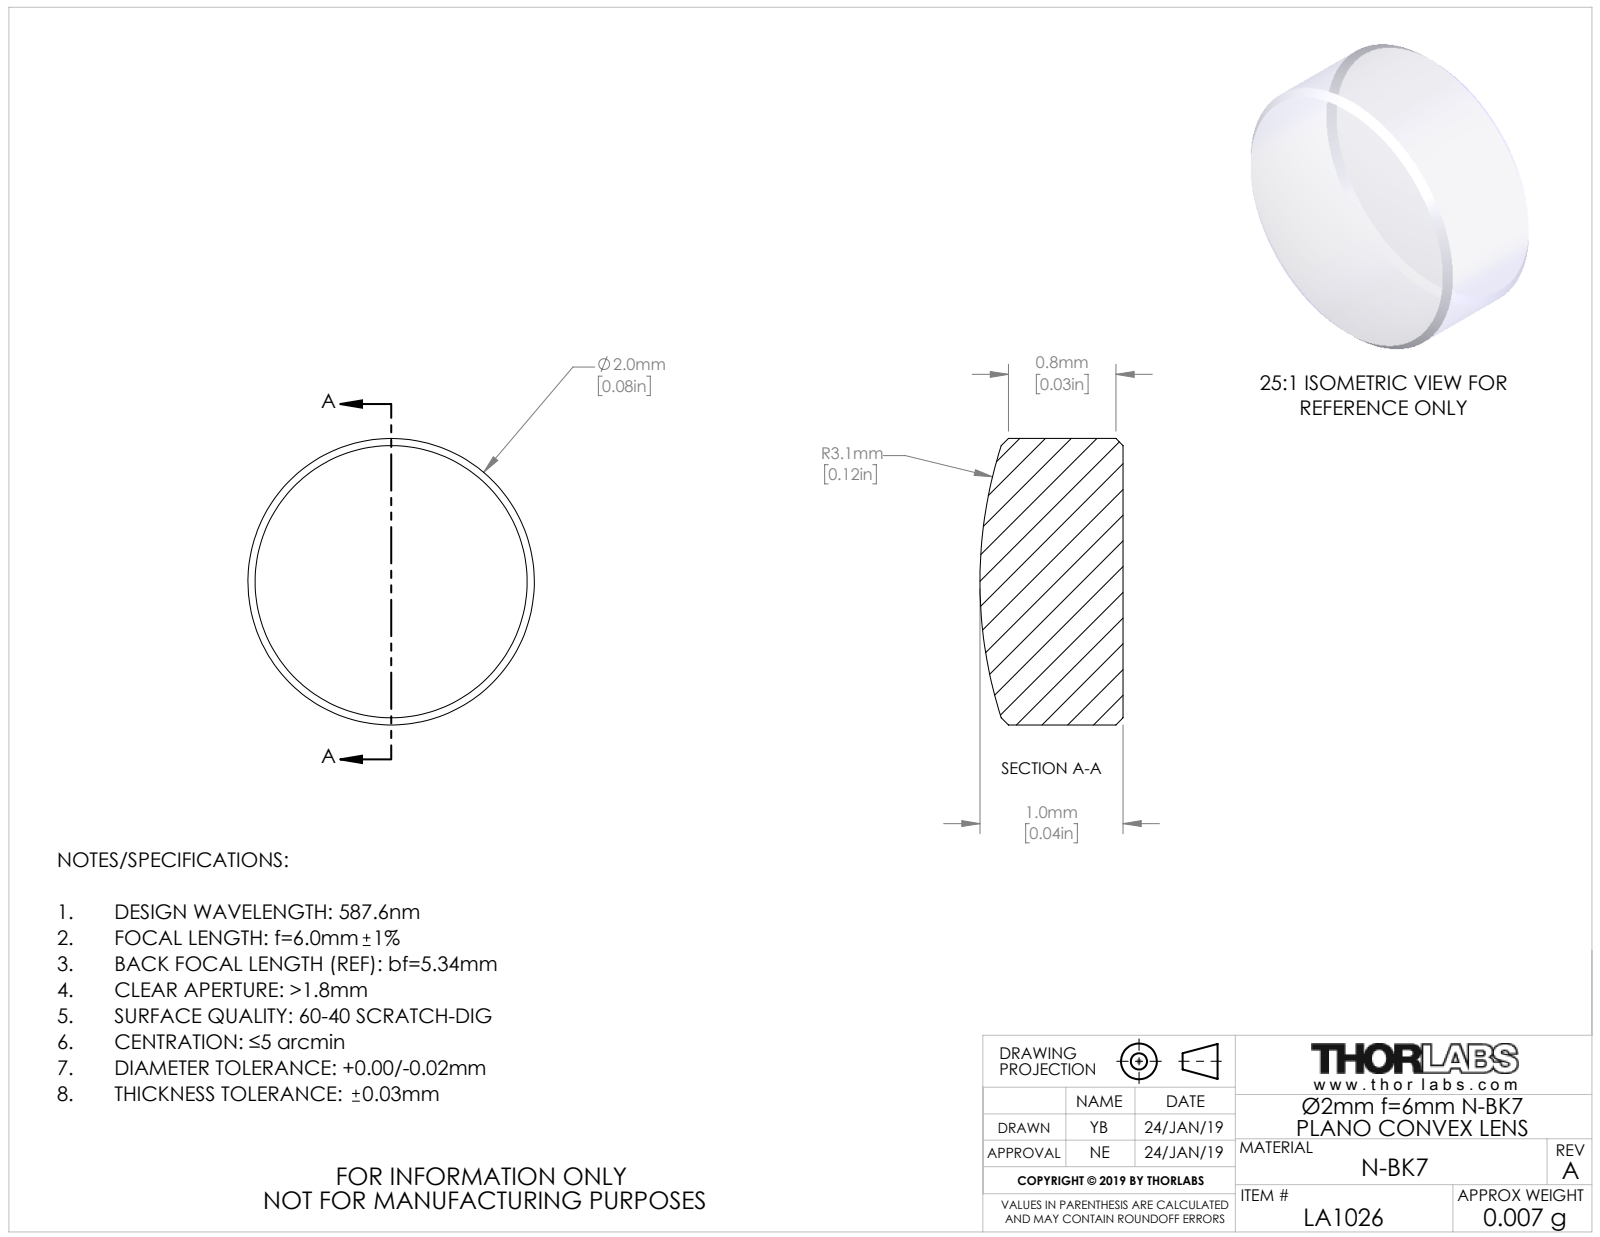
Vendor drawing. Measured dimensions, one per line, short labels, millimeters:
name: TTN162579-E0W
written by: SolidWorks 2018 (CONFIG_CONTROL_DESIGN)
unit: mm
bodies: 1 solid, 9 faces (1 planar, 2 cylindrical, 6 other)
size: 2 × 2 × 1
volume: 3 mm³; area: 11 mm²
bosses: 1× ⌀2
